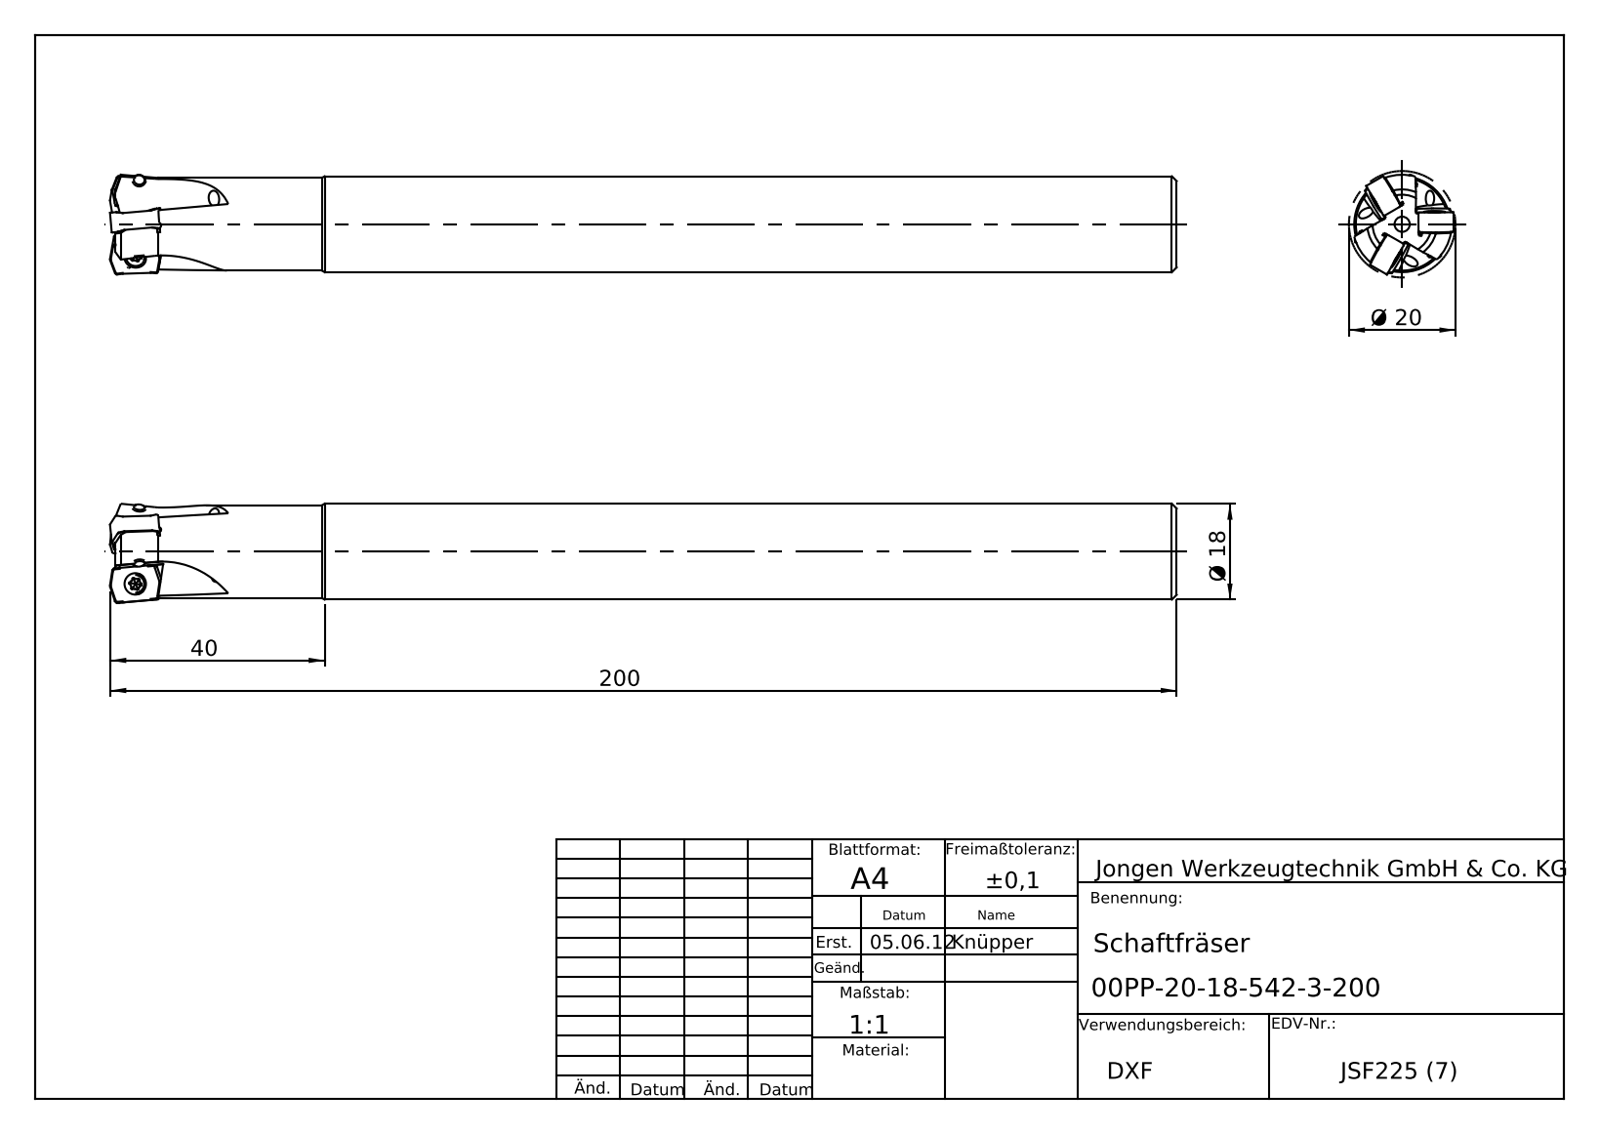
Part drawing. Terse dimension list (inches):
name: 00PP_20_18_542_3_200
written by: SolidWorks 2016 (AUTOMOTIVE_DESIGN)
unit: in
bodies: 1 solid, 62 faces (29 planar, 15 cylindrical, 18 other)
size: 7.874 × 0.787 × 0.787
volume: 2.911 in³; area: 22.53 in²
holes: 3× ⌀0.098, 1× ⌀0.157
bosses: 1× ⌀0.709, 1× ⌀0.685
rounds: 3× R0.591
face distances: 7.787, 0.163, 0.163, 0.02
